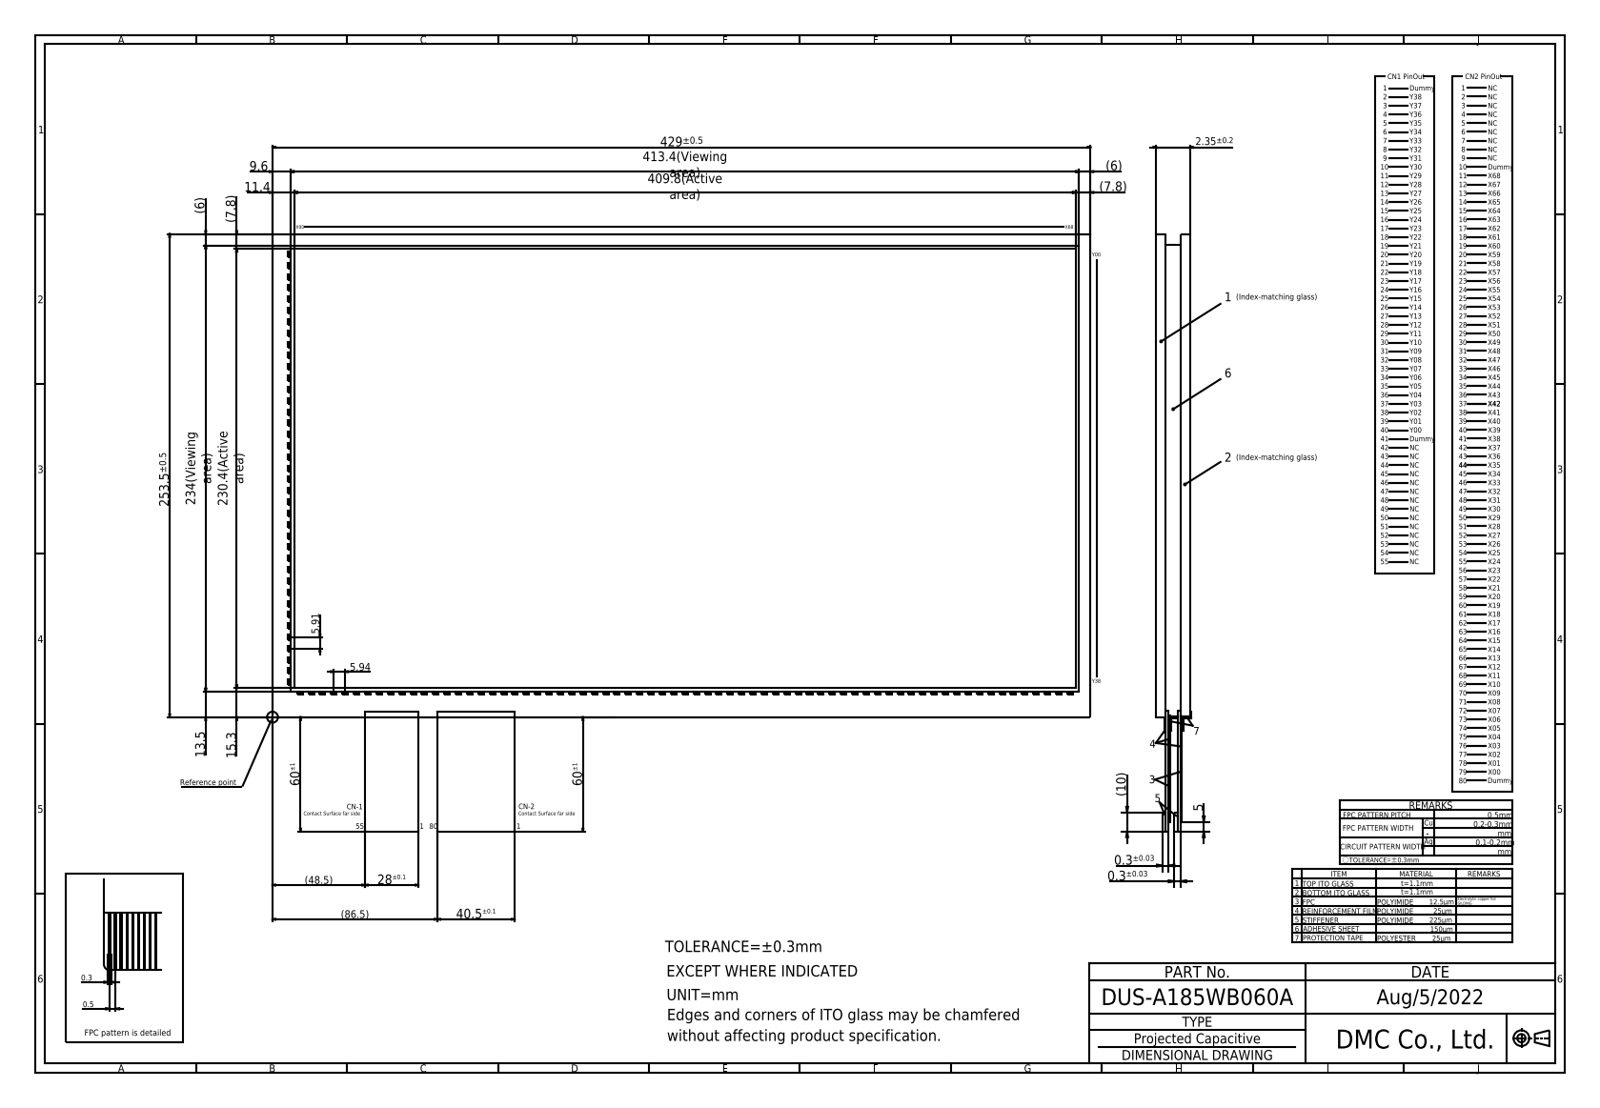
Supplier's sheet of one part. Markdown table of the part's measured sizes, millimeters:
| quantity | value |
| --- | --- |
| part name | DUS-A185WB060A |
| STEP written by | Autodesk Inventor 2020 (CONFIG_CONTROL_DESIGN) |
| units | millimeters |
| bodies | 1 solid, 578 faces (574 planar, 4 cylindrical, 0 other) |
| overall size | 600.6 × 364.2 × 2.35 |
| volume | 255 915 mm³ |
| surface area | 229 276 mm² |
| partial cylindrical surfaces (radius × count) | 0.2 × 4 |
| main face-to-face distances | 2.35, 1.1, 1.2, 1.15, 1.25, 1, 2.25, 253.5, 0.8, 0.7 |
